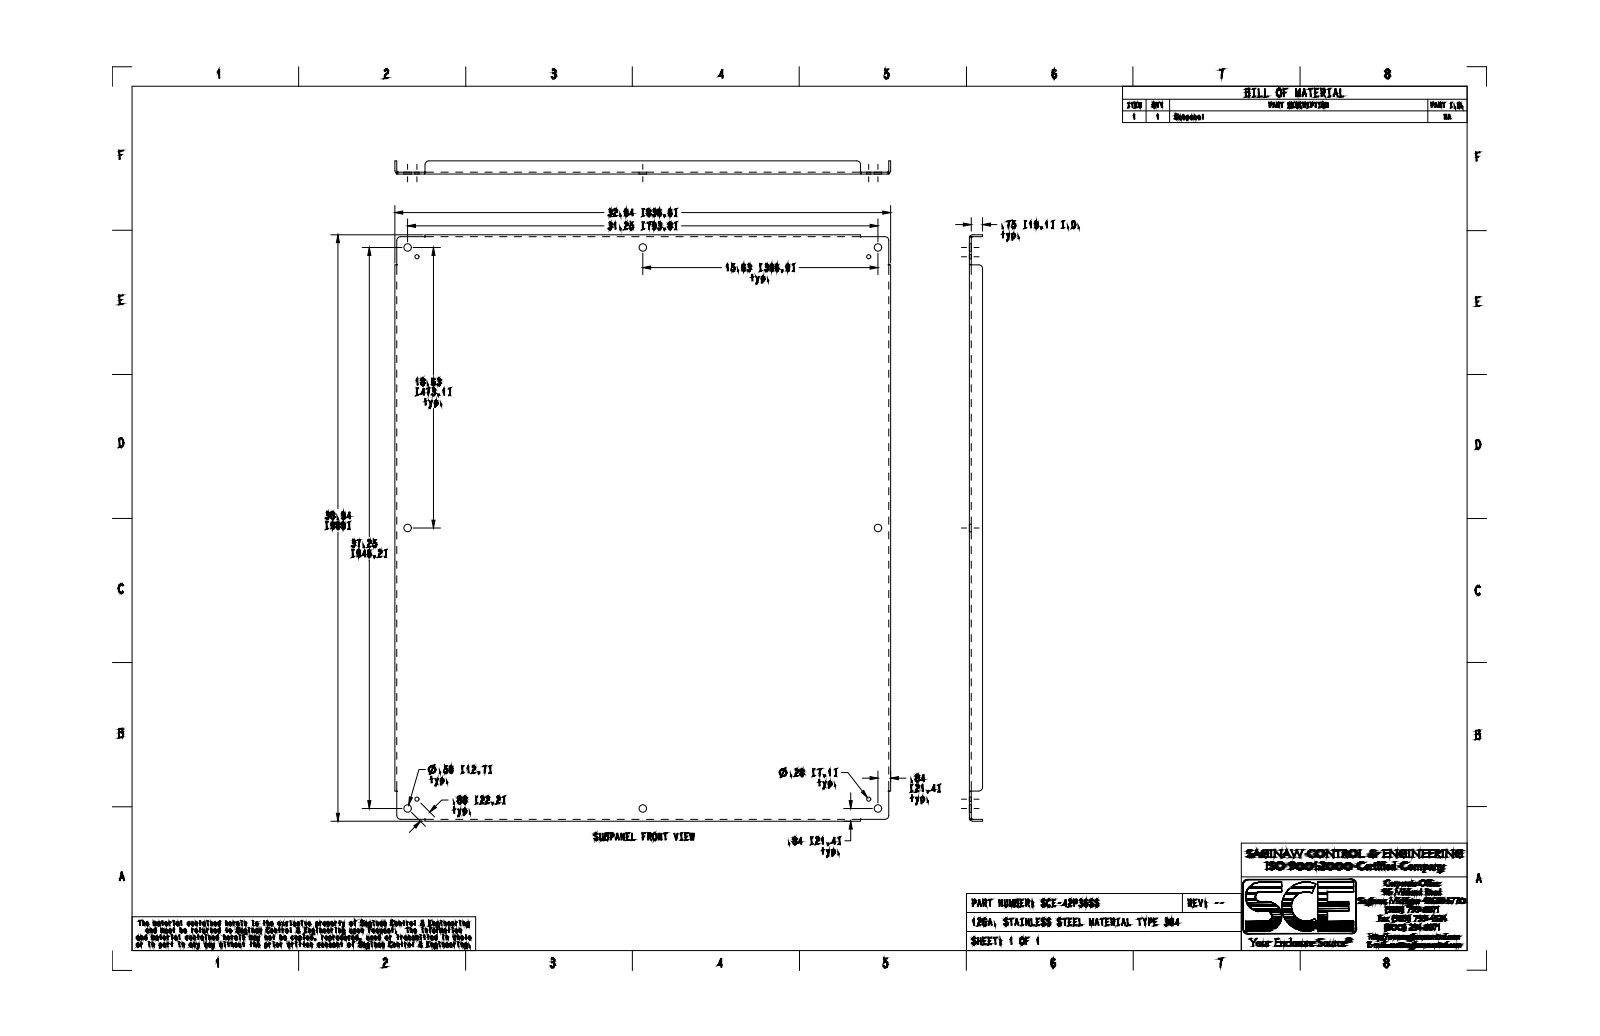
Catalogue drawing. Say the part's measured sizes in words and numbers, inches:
The part is named "SCE-42P36SS". Its 3-D file was written by "SolidWorks 2019 (CONFIG_CONTROL_DESIGN)". It is 1 solid with 86 faces: 30 planar, 32 cylindrical and 24 other. Overall it measures 38.938 by 32.938 by 0.875 inches. Its volume is 170.6 cubic inches and its surface area 2 750 square inches. Round holes: 8 of diameter 0.5, 4 of diameter 0.281. Partial cylindrical surfaces (rounded edges, fillets, slot ends): 8 of radius 0.25, 4 of radius 0.112, 4 of radius 0.237. The main face-to-face distances are 0.125, 0.125, 32.813, 38.813, 32.687, 32.938, 38.687, 38.938, 0.75, 0.875. The hole center spacings are 0.875, 15.019, 15.625, 18.017, 18.625, 24.311, 30.638, 35.532.
